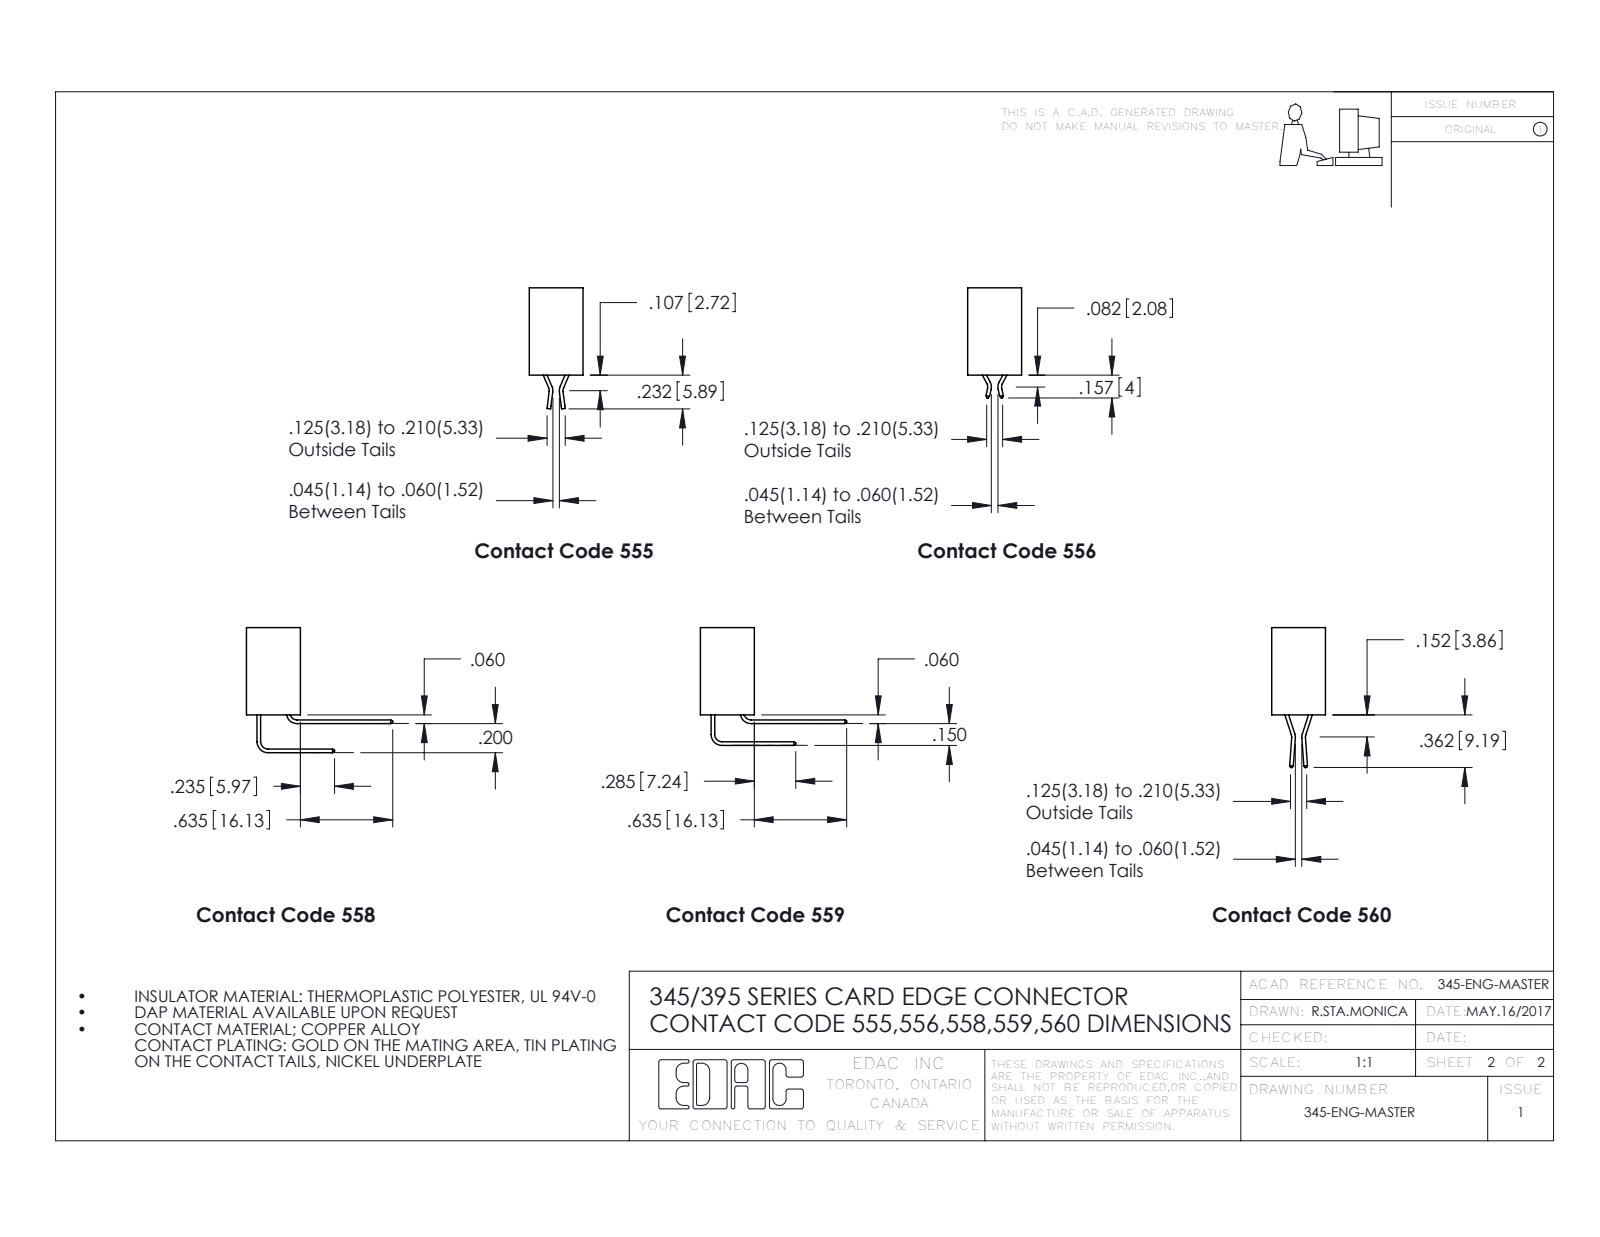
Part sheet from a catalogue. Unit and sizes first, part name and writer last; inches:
Units: inches
Overall size (bounding box): 6.56 × 0.737 × 0.37
Round holes (diameter × count): ⌀0.064 ×1
Partial cylindrical surfaces — rounded edges, fillets, slot ends (radius × count): R0.006 ×252, R0.01 ×22, R0.007 ×6, R0.031 ×6, R0.026 ×3, R0.014 ×2, R0.019 ×2, R0.022 ×2
Main face-to-face distances: 0.298, 0.072, 0.2, 0.37, 0.098, 0.272, 0.025, 0.225, 0.072, 0.175
Volume: 1.025 in³ · Surface area: 38.6 in²
Bodies: 127 solids, 6922 faces (4990 planar, 1932 cylindrical, 0 other)
Part name (STEP PRODUCT): 345 Part_No Mounting Lugs; 345-292-001_345-293-125; 345-126-525-201
STEP written by: SolidWorks 2020 (CONFIG_CONTROL_DESIGN)
